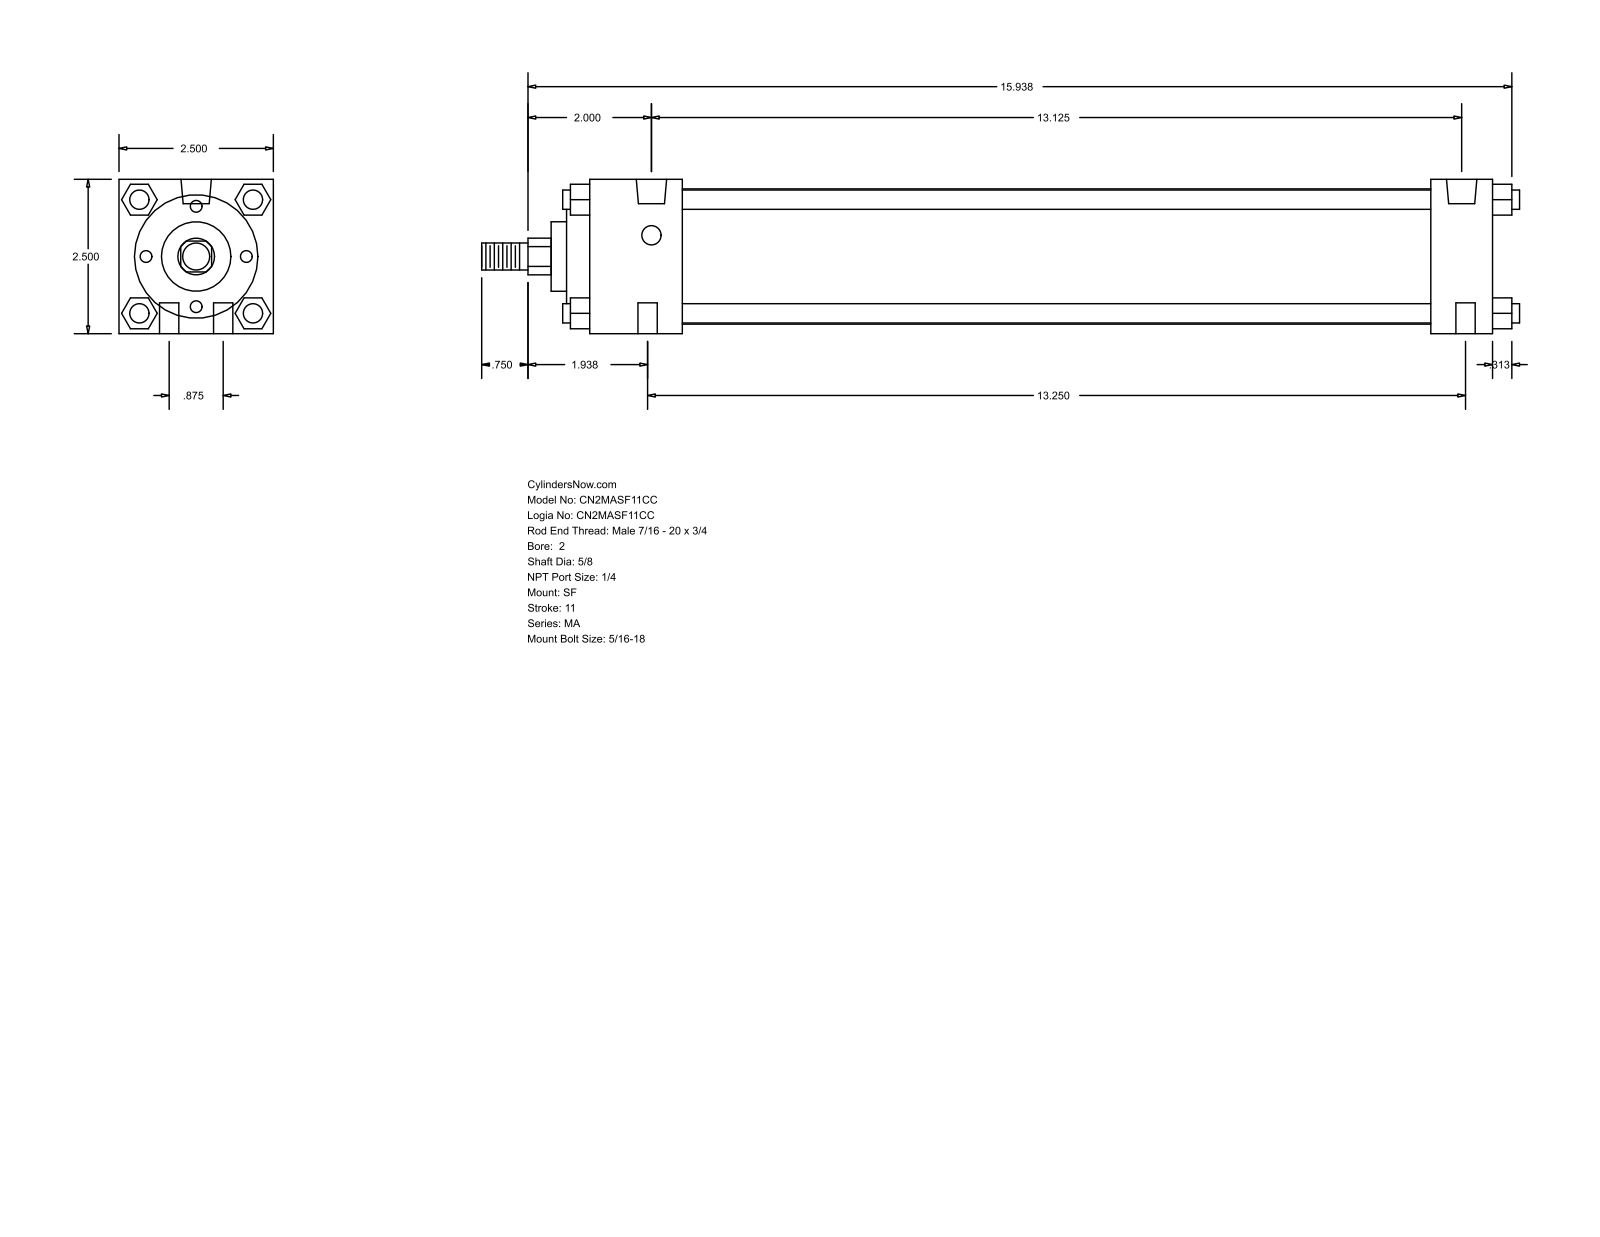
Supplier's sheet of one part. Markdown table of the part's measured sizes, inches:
| quantity | value |
| --- | --- |
| part name | MA_SF__0200_0.625 |
| STEP written by | GSSL Pune (CONFIG_CONTROL_DESIGN) |
| units | inches |
| bodies | 0 solids, 126 faces (95 planar, 31 cylindrical, 0 other) |
| overall size | 16.813 × 2.5 × 2.5 |
| round holes (diameter × count) | 0.313 × 6, 0.492 × 2 |
| round bosses / shafts (diameter × count) | 0.313 × 4, 2.19 × 1, 2 × 1, 1.125 × 1, 0.625 × 1, 0.437 × 1 |
| partial cylindrical surfaces (radius × count) | 0.297 × 1 |
| main face-to-face distances | 2.5, 1, 0.5, 1.5, 14.625, 13.625, 12.125, 13.125, 0.375, 1.875 |
| hole center spacings | 0.442, 0.875, 13.125, 13.194, 13.195, 13.25, 13.279 |
